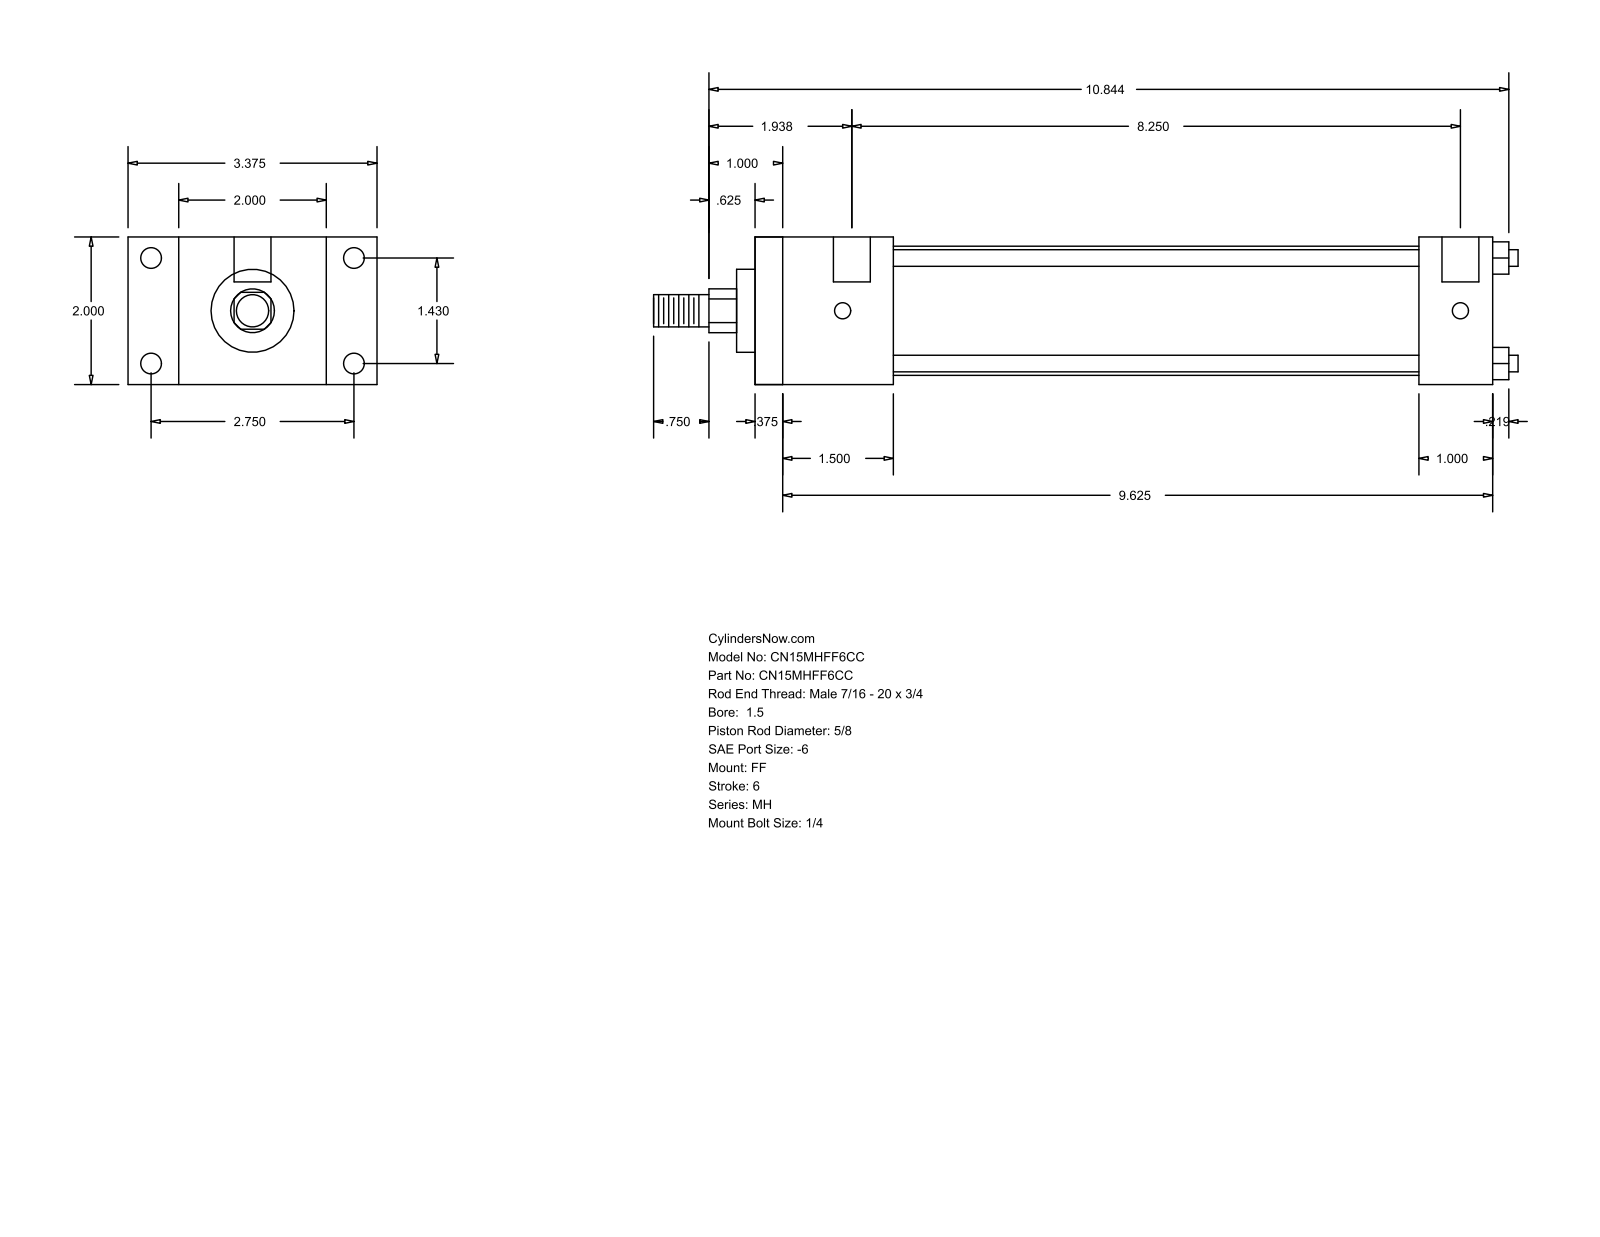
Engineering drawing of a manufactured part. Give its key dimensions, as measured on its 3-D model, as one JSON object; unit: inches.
{"part_name": "MH_FF__0150_0.625", "step_written_by": "GSSL Pune (CONFIG_CONTROL_DESIGN)", "units": "inches", "bodies": {"solids": 0, "faces": 92, "planar": 64, "cylindrical": 28, "other": 0}, "overall_size": [11.719, 3.375, 2], "round_holes": [[0.219, 4], [0.281, 4], [0.5, 2]], "round_bosses_or_shafts": [[0.225, 4], [1.75, 1], [1.125, 1], [0.625, 1], [0.437, 1]], "partial_cylinders_radius": [[0.297, 1]], "face_to_face_distances": [2, 10, 0.375, 9.625, 0.687, 2.687, 1.875, 1.5, 8.125, 9], "hole_center_spacings": [1.43, 2.75, 3.099, 8.375, 0.125, 8.25]}
